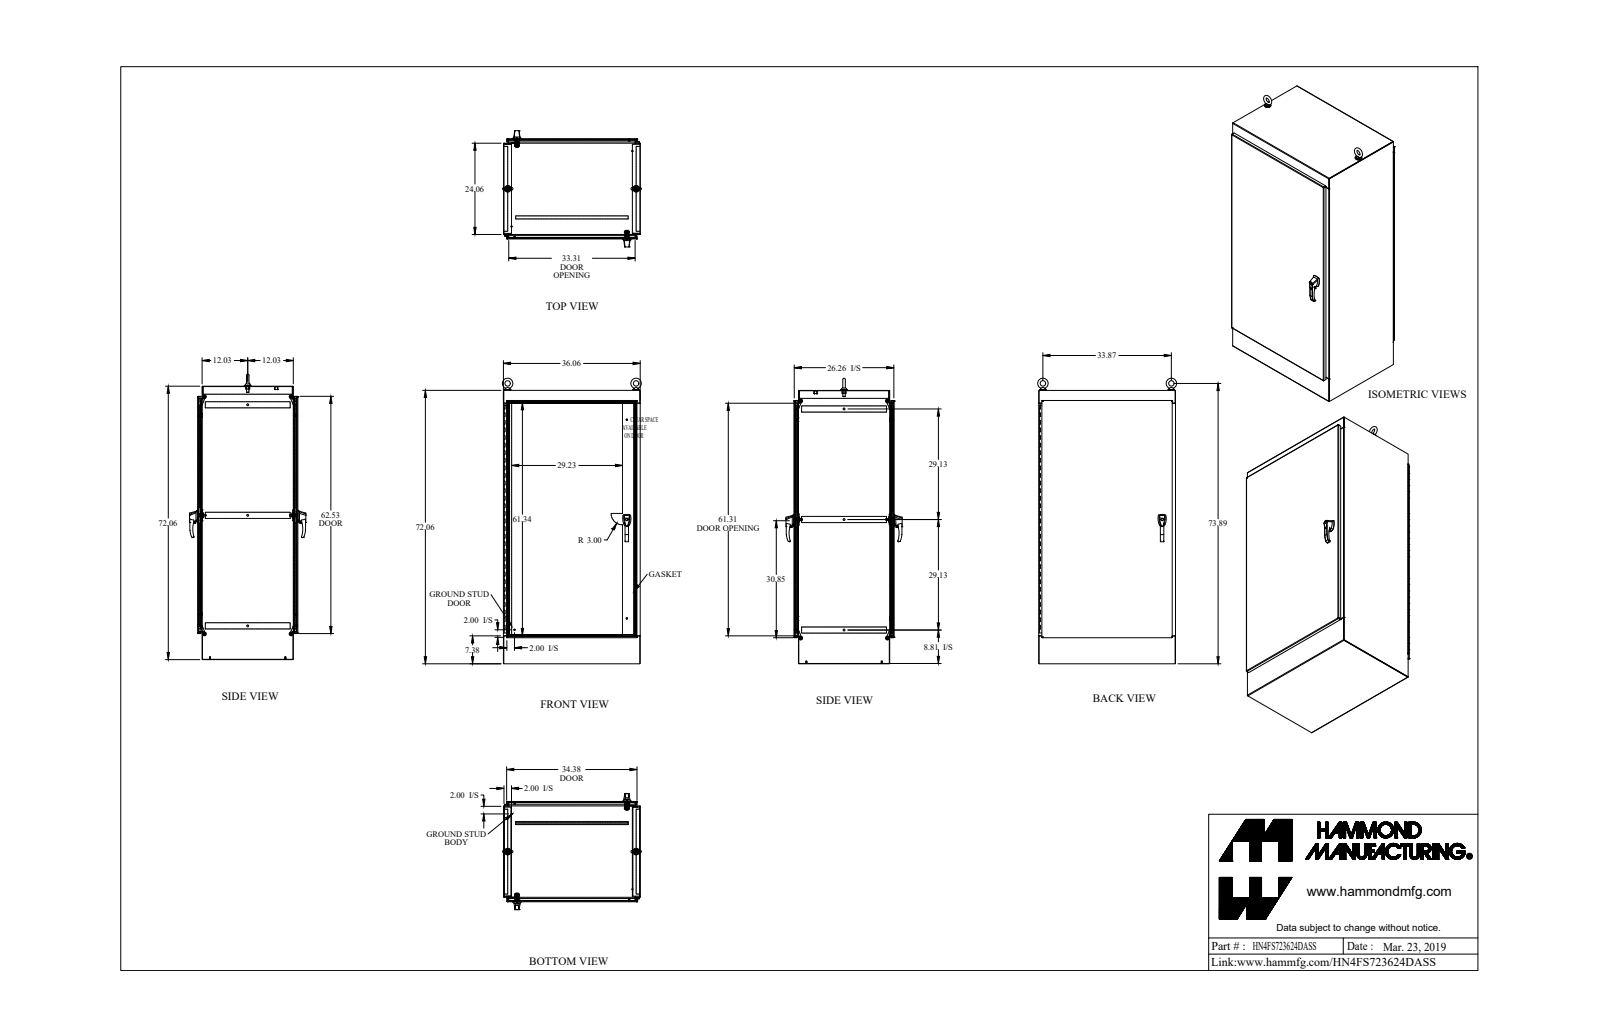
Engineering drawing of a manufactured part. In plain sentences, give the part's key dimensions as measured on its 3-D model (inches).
The part is named "HN4FS723624DASS". Its 3-D file was written by "SolidWorks 2018 (AUTOMOTIVE_DESIGN)". It is 85 solids with 3193 faces: 1440 planar, 1485 cylindrical and 268 other. Overall it measures 75.489 by 36.604 by 30.664 inches. Its volume is 1 270 cubic inches and its surface area 26 786 square inches. Round holes: 20 of diameter 0.304, 8 of diameter 0.35, 4 of diameter 0.25, 4 of diameter 0.257, 4 of diameter 0.28, 4 of diameter 0.281, 4 of diameter 0.313, 4 of diameter 0.39, 4 of diameter 0.413, 3 of diameter 0.5, 2 of diameter 0.11, 2 of diameter 0.173. Round bosses or shafts: 4 of diameter 1, 4 of diameter 0.75, 4 of diameter 0.63, 4 of diameter 0.625, 4 of diameter 0.44, 4 of diameter 0.37, 4 of diameter 0.313, 4 of diameter 0.281. Partial cylindrical surfaces (rounded edges, fillets, slot ends): 44 of radius 0.125, 42 of radius 0.043, 36 of radius 0.138, 32 of radius 0.018, 26 of radius 0.048, 26 of radius 0.143, 26 of radius 0.5, 21 of radius 0.06. The main face-to-face distances are 0.095, 26.339, 35.965, 26.244, 26.434, 1.187, 25.152, 35.87, 36.06, 71.965. The hole center spacings are 6, 34.849, 12, 36.365, 18, 38.761, 24, 41.886.
